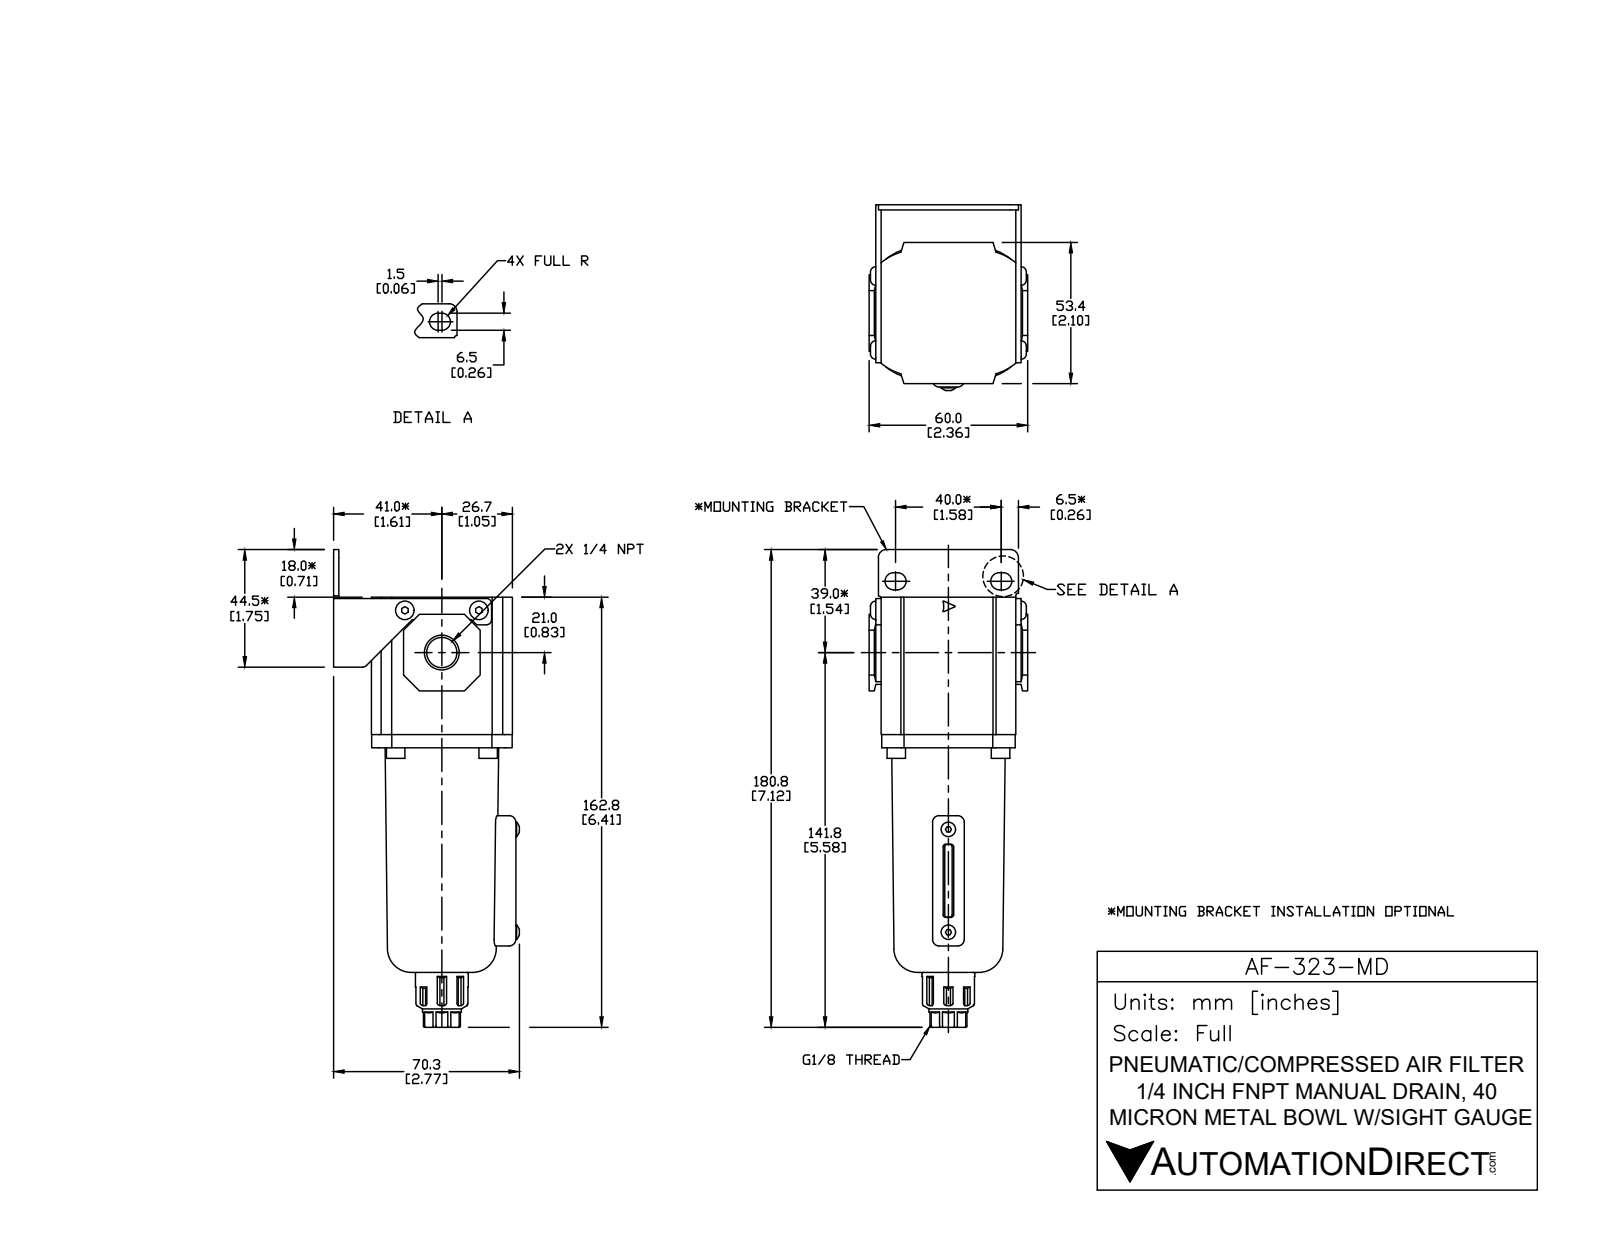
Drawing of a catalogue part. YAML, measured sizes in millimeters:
part_name: "AF-323-MD"
step_written_by: "SolidWorks 2015 (CONFIG_CONTROL_DESIGN)"
units: millimeters
bodies: {solids: 9, faces: 412, planar: 245, cylindrical: 98, other: 69}
overall_size: [181.1, 71, 60]
volume: 278055
surface_area: 49434
round_holes:
  - {diameter: 3.4, count: 2}
  - {diameter: 6.2, count: 1}
  - {diameter: 11.13, count: 1}
round_bosses_or_shafts:
  - {diameter: 7, count: 4}
  - {diameter: 5.5, count: 2}
  - {diameter: 20, count: 1}
  - {diameter: 14.7, count: 1}
partial_cylinders:
  - {radius: 1.3, count: 8}
  - {radius: 2.5, count: 8}
  - {radius: 9.5, count: 8}
  - {radius: 0.5, count: 6}
  - {radius: 2, count: 5}
  - {radius: 0.3, count: 4}
  - {radius: 1, count: 4}
  - {radius: 3.25, count: 4}
face_to_face_distances: [2, 52, 51, 53, 53.4, 12.3, 14.3, 67.7, 65.7, 2.5]
hole_center_spacings: [21.06, 21.46, 28]
